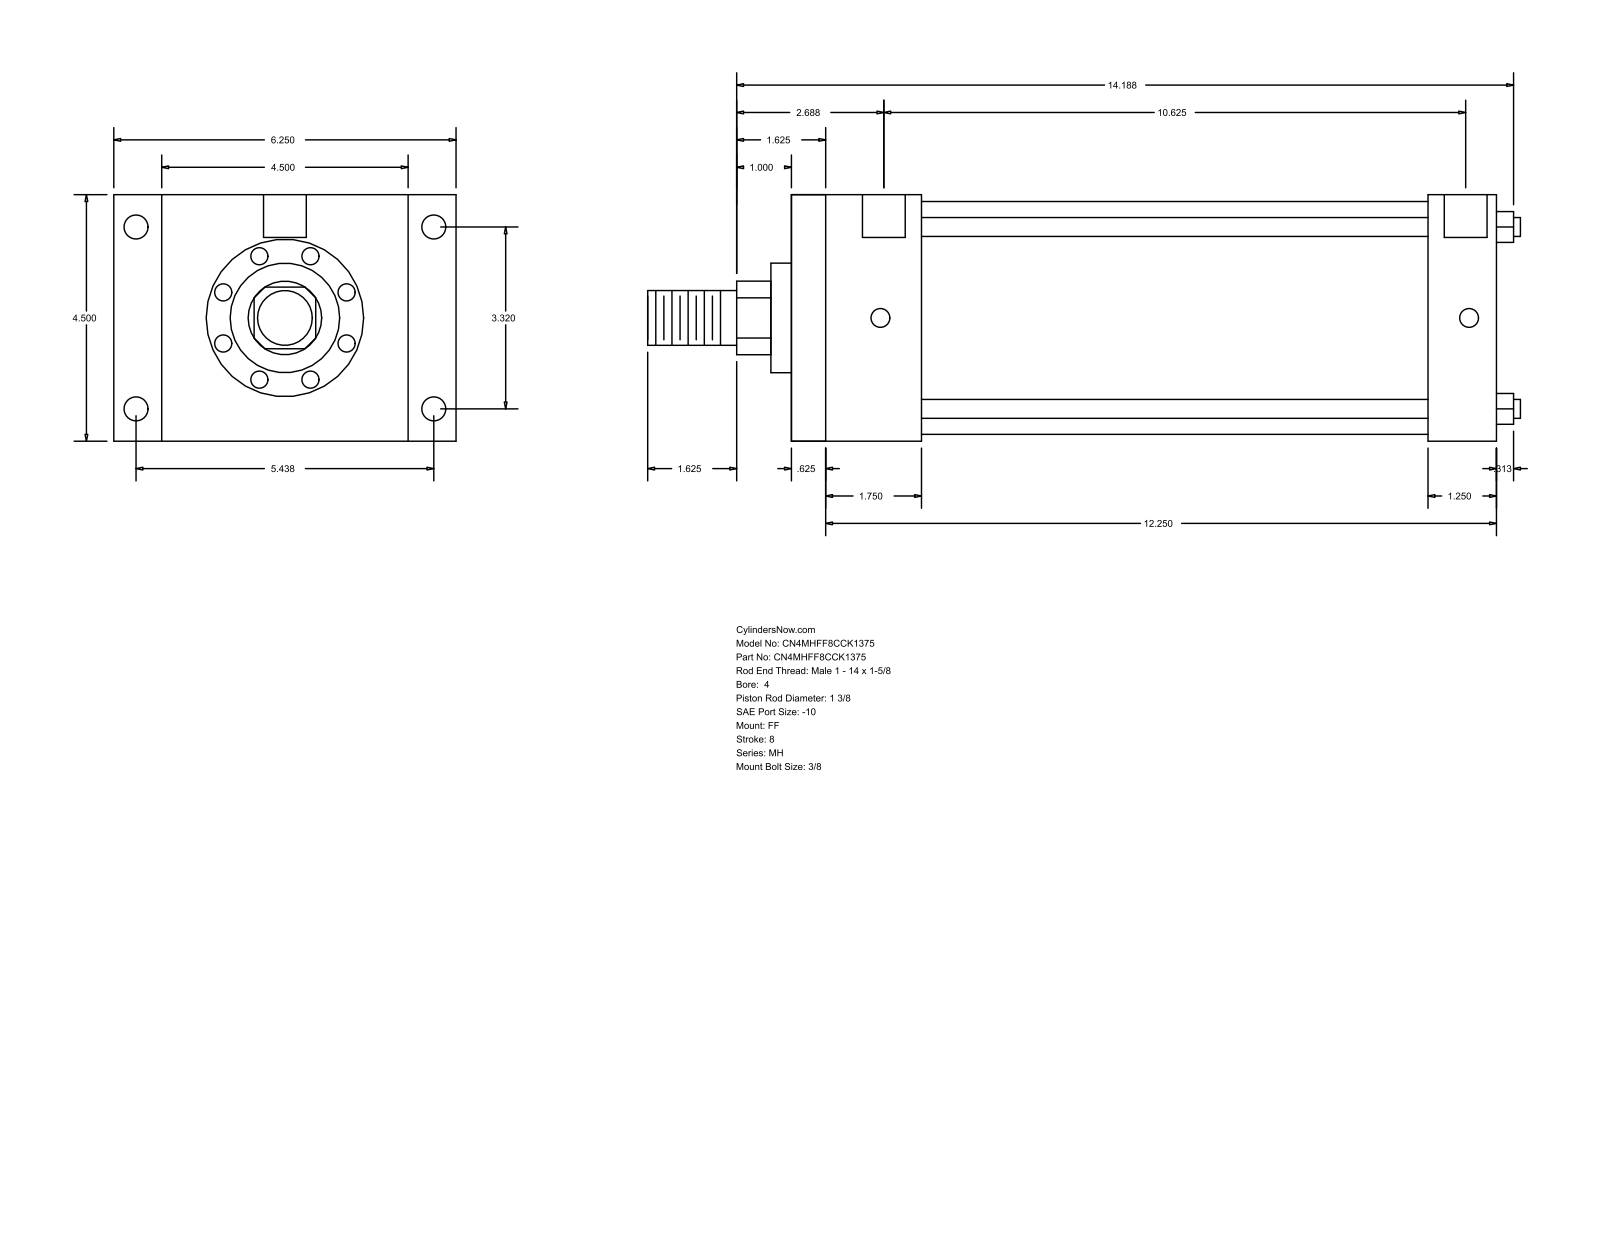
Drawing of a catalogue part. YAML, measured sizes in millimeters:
part_name: "MH_FF__0400_1.375"
step_written_by: "GSSL Pune (CONFIG_CONTROL_DESIGN)"
units: millimeters
bodies: {solids: 0, faces: 92, planar: 64, cylindrical: 28, other: 0}
overall_size: [404.81, 158.75, 114.3]
round_holes:
  - {diameter: 8.73, count: 4}
  - {diameter: 11.13, count: 4}
  - {diameter: 19.84, count: 2}
round_bosses_or_shafts:
  - {diameter: 8.76, count: 4}
  - {diameter: 107.95, count: 1}
  - {diameter: 50.8, count: 1}
  - {diameter: 34.92, count: 1}
  - {diameter: 25.4, count: 1}
partial_cylinders:
  - {radius: 17.06, count: 1}
face_to_face_distances: [114.3, 327.03, 15.87, 311.16, 60.32, 44.45, 266.71, 295.28, 279.41, 234.96]
hole_center_spacings: [1.59, 84.32, 138.12, 161.82, 271.47, 273.06, 269.88]
